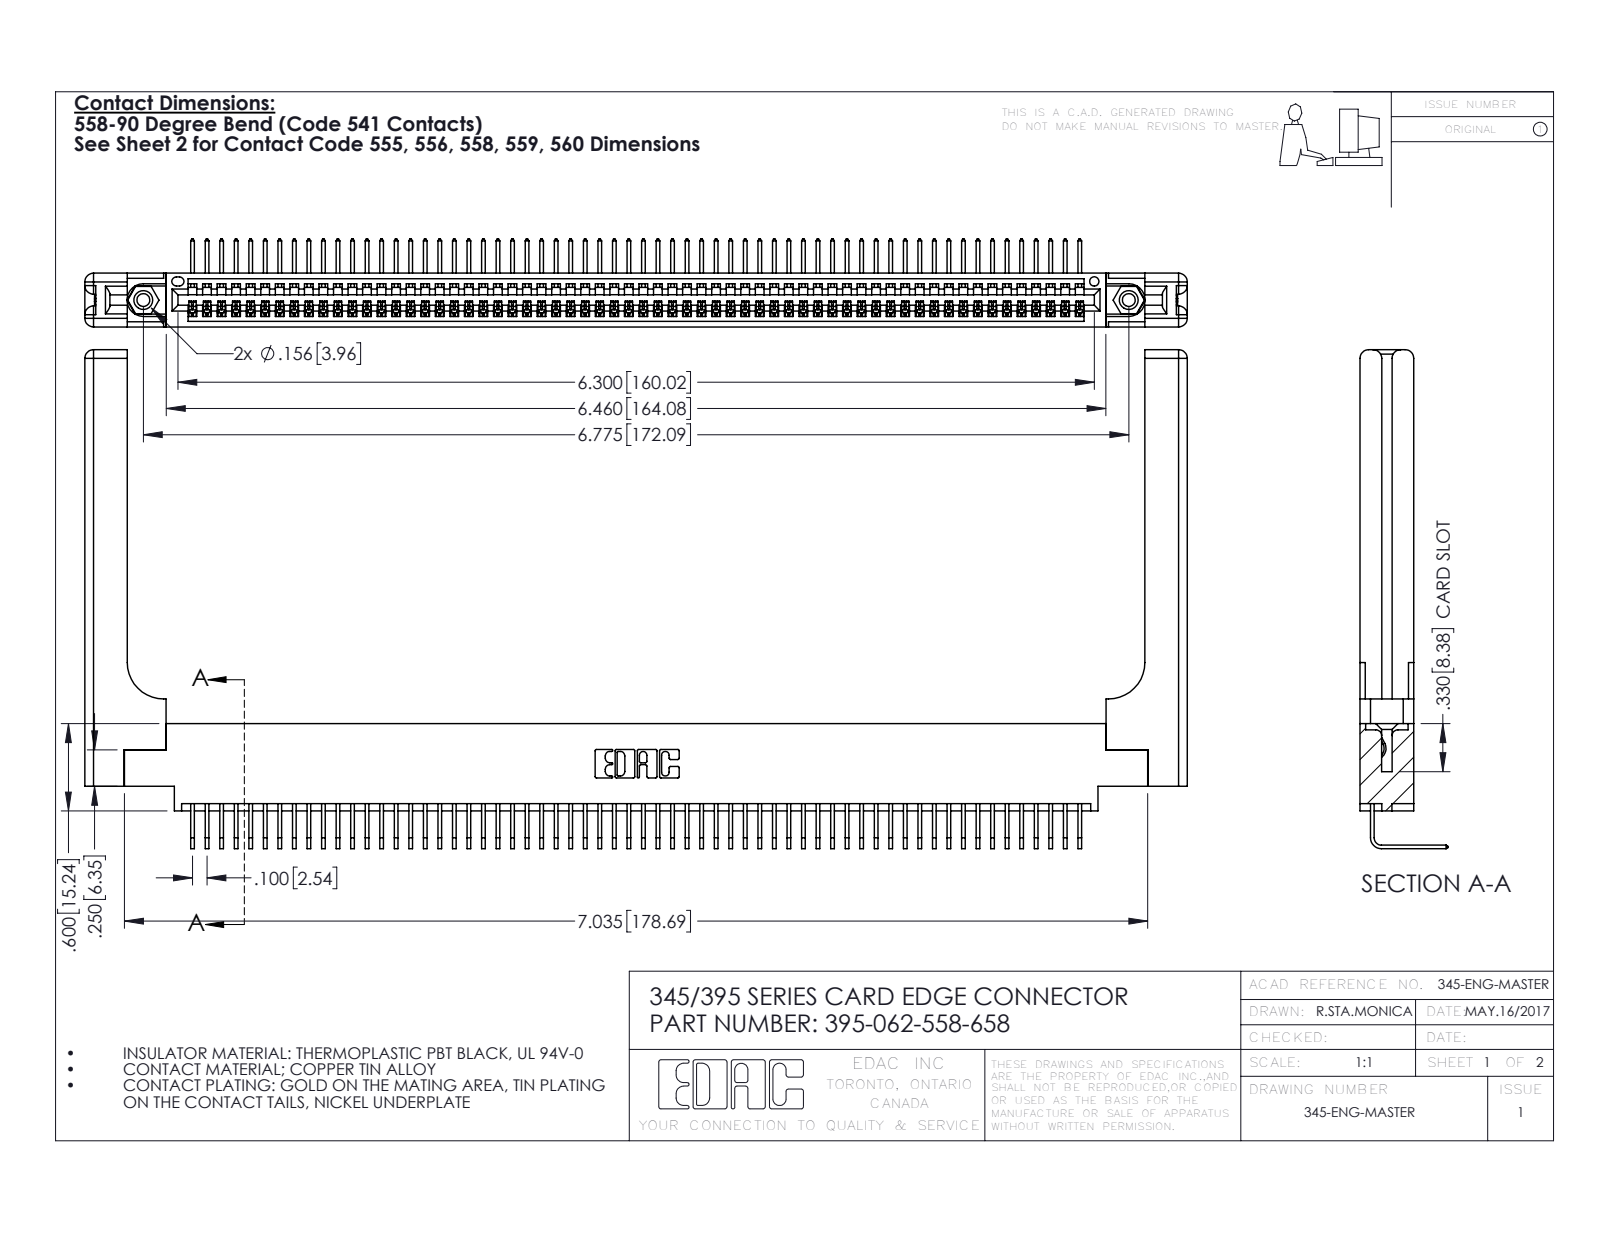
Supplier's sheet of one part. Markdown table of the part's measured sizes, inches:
| quantity | value |
| --- | --- |
| part name | 345-220-058_345-220-058; 345-250-001_345-250-001-102; 345-292-001_558 Tail - 2; 345 Part_0.170 Offset - 0.156 Dia-TH (+1 more) |
| STEP written by | SolidWorks 2016 (CONFIG_CONTROL_DESIGN) |
| units | inches |
| bodies | 67 solids, 4106 faces (2836 planar, 1210 cylindrical, 60 other) |
| overall size | 7.579 × 3.429 × 0.605 |
| volume | 1.65 in³ |
| surface area | 48.91 in² |
| round holes (diameter × count) | 0.089 × 2, 0.125 × 2, 0.156 × 2, 0.064 × 1 |
| round bosses / shafts (diameter × count) | 0.155 × 2 |
| partial cylindrical surfaces (radius × count) | 0.006 × 124, 0.01 × 22, 0.06 × 16, 0.007 × 6, 0.031 × 6, 0.026 × 3, 0.03 × 2, 0.031 × 2 |
| main face-to-face distances | 0.072, 0.37, 0.298, 0.098, 0.272, 0.025, 0.2, 0.225, 0.15, 0.148 |
| hole center spacings | 0.27, 6.539, 6.775 |
